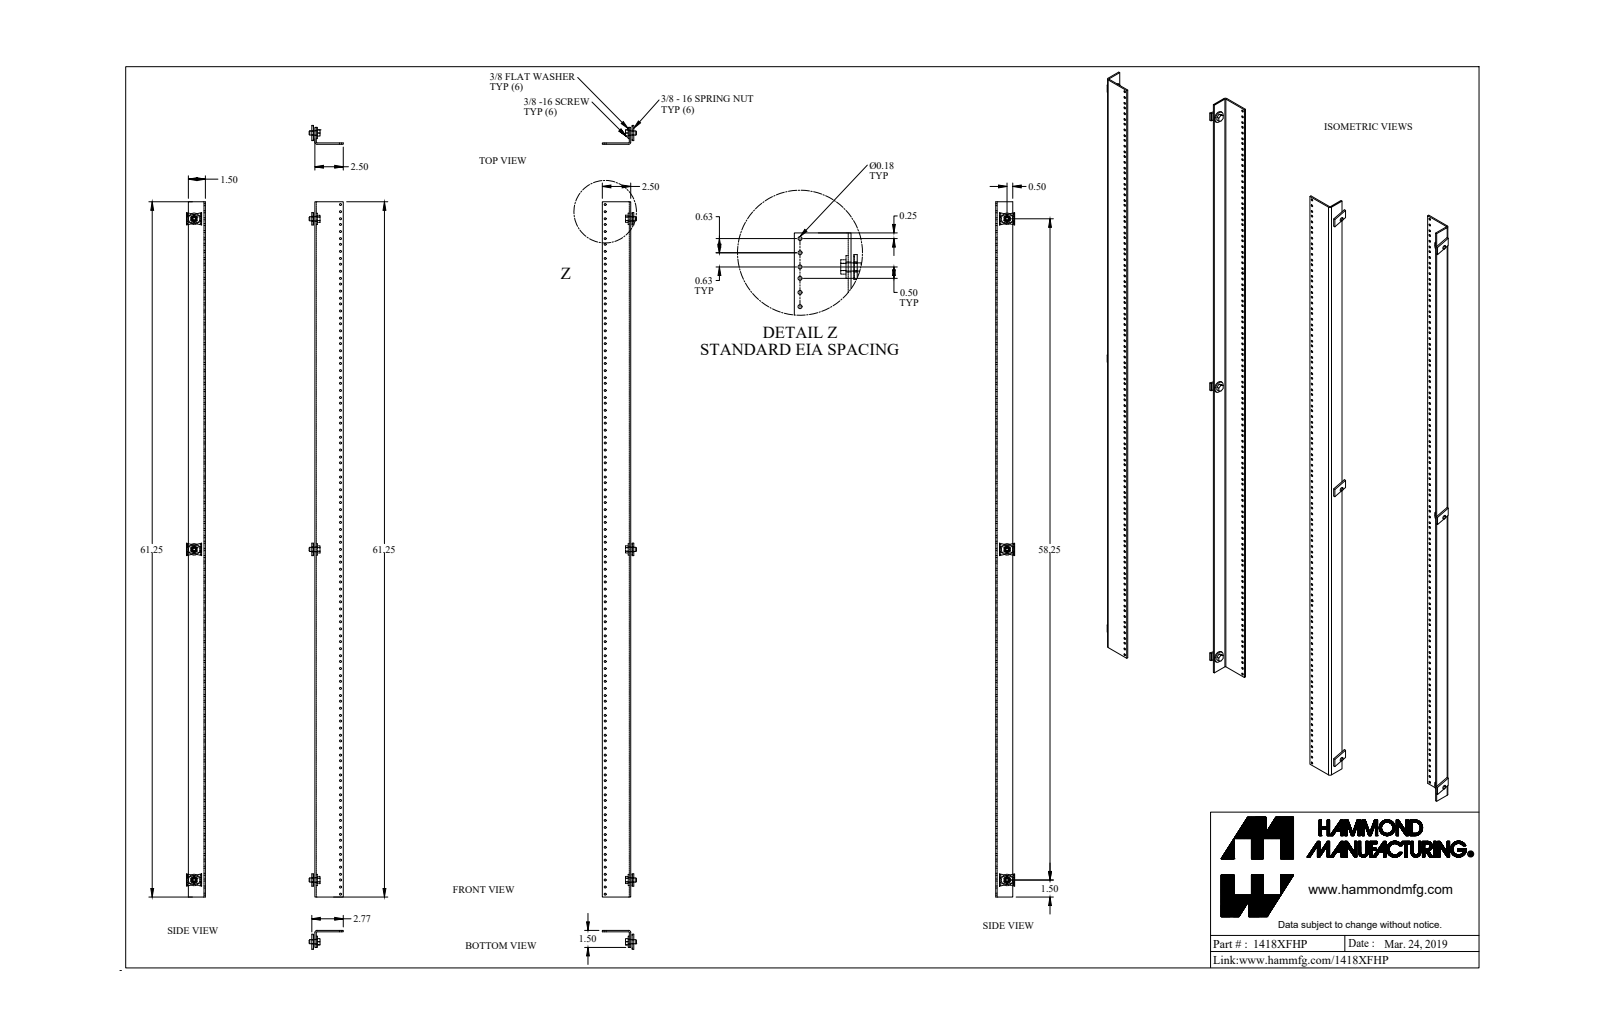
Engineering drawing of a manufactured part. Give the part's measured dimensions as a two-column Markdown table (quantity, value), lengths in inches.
| quantity | value |
| --- | --- |
| part name | 1418XFHP_Default |
| STEP written by | SolidWorks 2019 (CONFIG_CONTROL_DESIGN) |
| units | inches |
| bodies | 20 solids, 674 faces (178 planar, 484 cylindrical, 12 other) |
| overall size | 61.25 × 28.856 × 1.668 |
| volume | 59.77 in³ |
| surface area | 1 010 in² |
| round holes (diameter × count) | 0.177 × 210, 0.313 × 3, 0.437 × 3, 0.445 × 3 |
| round bosses / shafts (diameter × count) | 1 × 3, 0.36 × 3 |
| partial cylindrical surfaces (radius × count) | 0.06 × 2, 0.185 × 2 |
| main face-to-face distances | 0.125, 0.125, 27.84, 27.59, 27.715, 27.715, 1.5, 1.375, 1.375, 2.5 |
| hole center spacings | 1.75, 5.25, 3.5, 2.375, 0.625, 4.125, 8.75, 1.125 |
